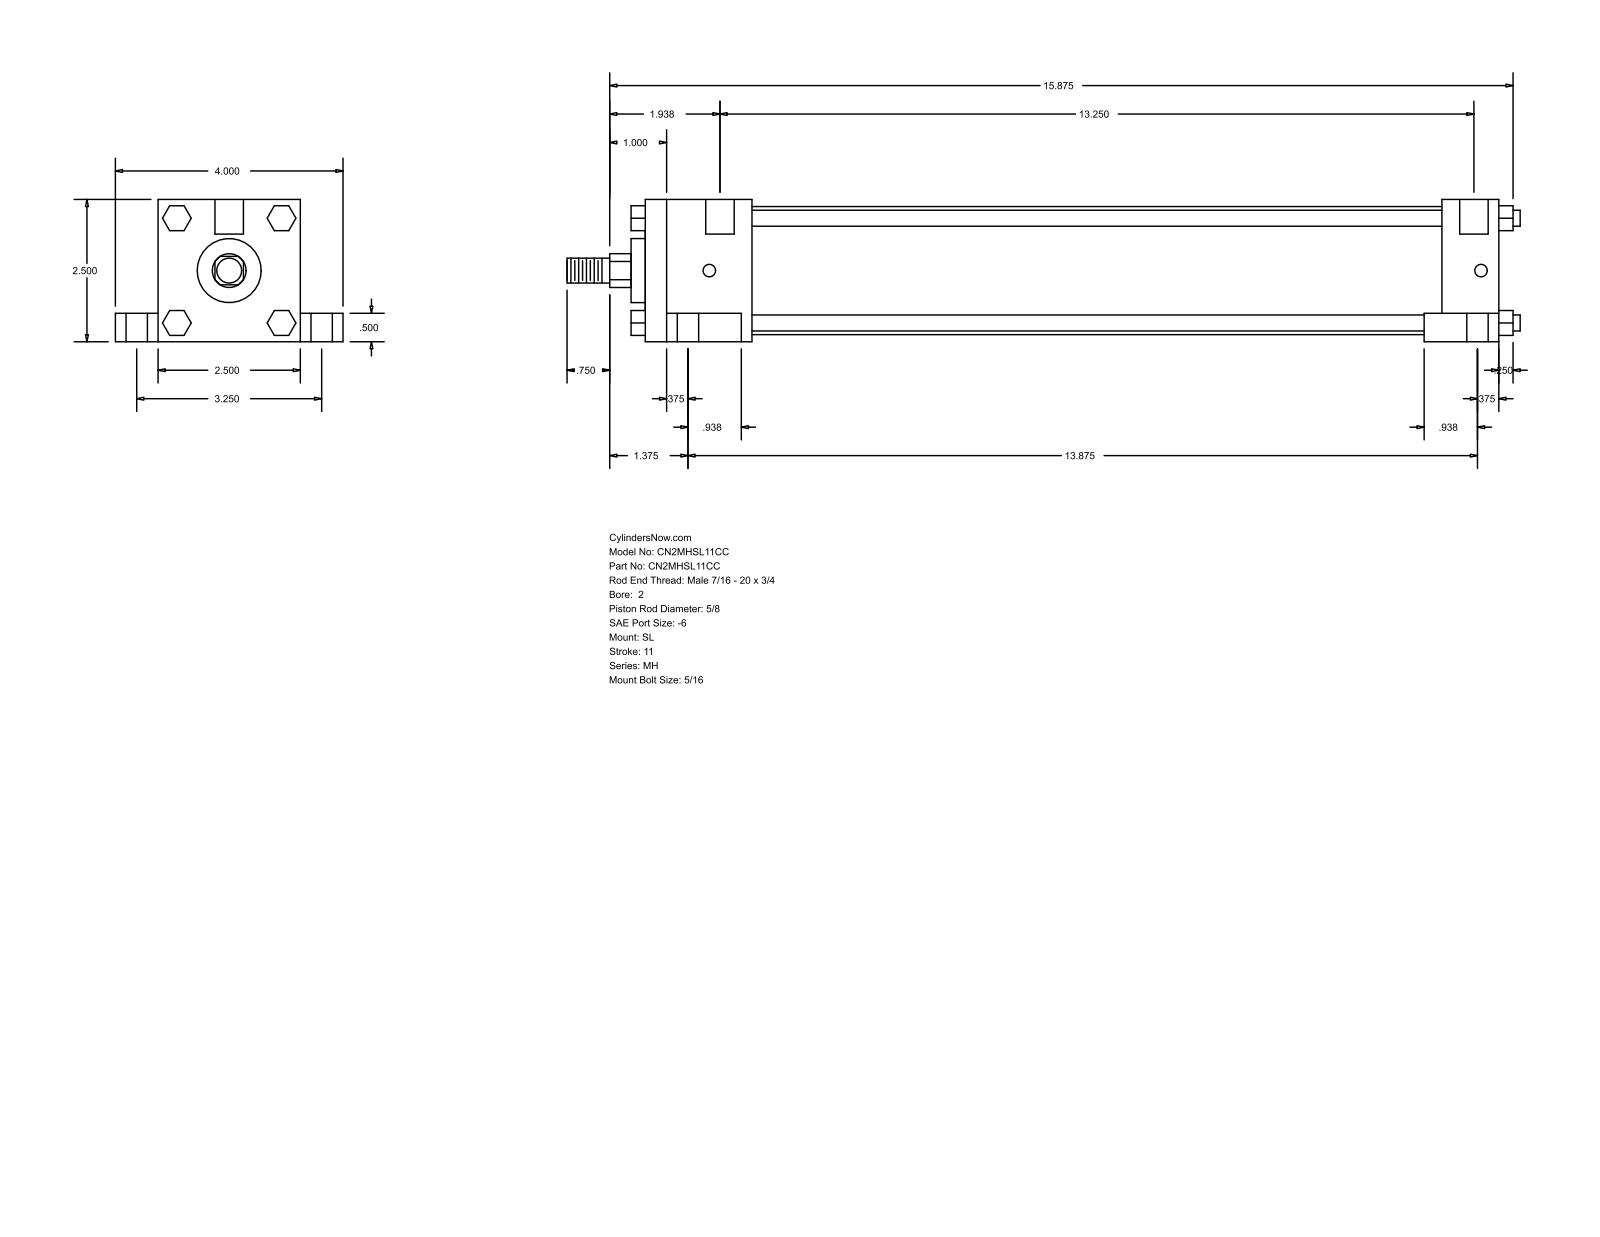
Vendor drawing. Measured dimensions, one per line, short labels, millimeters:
name: MH_SL__0200_0.625
written by: GSSL Pune (CONFIG_CONTROL_DESIGN)
unit: mm
bodies: 0 solids, 148 faces (112 planar, 36 cylindrical, 0 other)
size: 425.45 × 101.6 × 63.5
holes: 4× ⌀5.56, 4× ⌀9.53, 4× ⌀15.88, 2× ⌀12.7
bosses: 4× ⌀7.14, 1× ⌀57.15, 1× ⌀28.57, 1× ⌀15.88, 1× ⌀11.11
rounds: 1× R7.54
face distances: 63.5, 381, 12.7, 19.05, 82.55, 50.8, 25.4, 355.6, 47.62, 307.98
hole spacings: 41.3, 42.36, 43.67, 82.54, 340.65, 344.49, 345.37, 352.43
